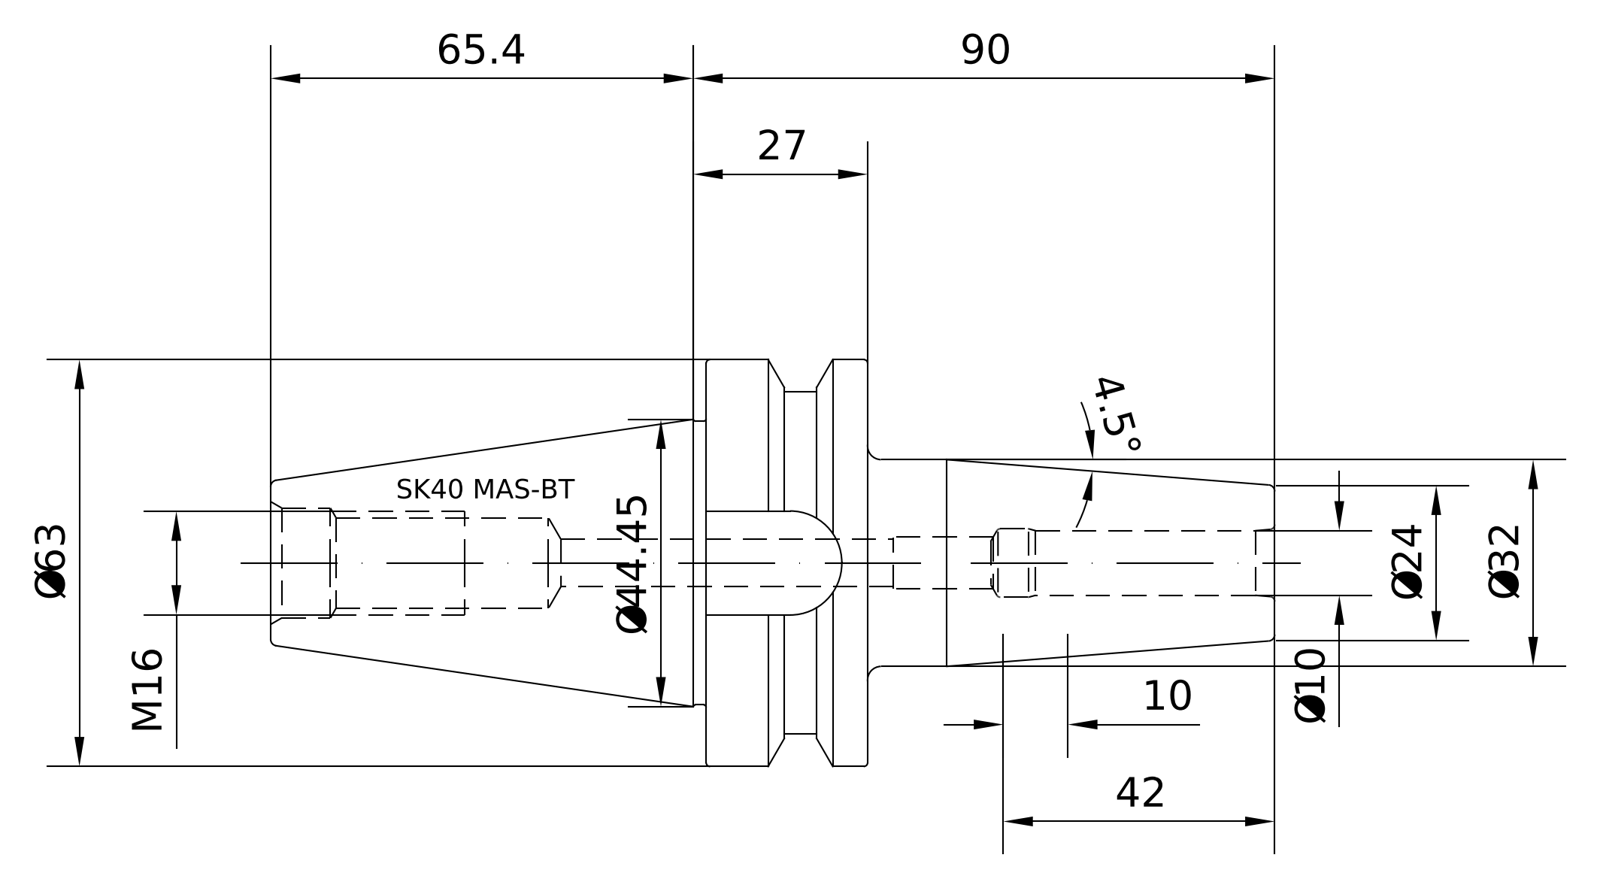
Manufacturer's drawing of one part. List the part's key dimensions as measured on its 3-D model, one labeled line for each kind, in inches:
Part name (STEP PRODUCT): 40-640-10
STEP written by: PRO/ENGINEER BY PARAMETRIC TECHNOLOGY CORPORATION, 2010430 (CONFIG_CONTROL_DESIGN)
Units: inches
Bodies: 1 solid, 96 faces (26 planar, 22 cylindrical, 48 other)
Overall size (bounding box): 6.118 × 2.48 × 2.48
Volume: 10.02 in³ · Surface area: 44.02 in²
Round holes (diameter × count): ⌀0.394 ×1, ⌀0.545 ×1, ⌀0.67 ×1, ⌀0.689 ×1
Round bosses / shafts (diameter × count): ⌀2.48 ×1, ⌀2.077 ×1, ⌀1.722 ×1, ⌀1.26 ×1, ⌀0.63 ×1
Partial cylindrical surfaces — rounded edges, fillets, slot ends (radius × count): R0.319 ×1
Main face-to-face distances: 0.984, 1.768, 3.465, 2.48, 0.638, 2.654, 3.638, 6.118, 4.465, 1.811
